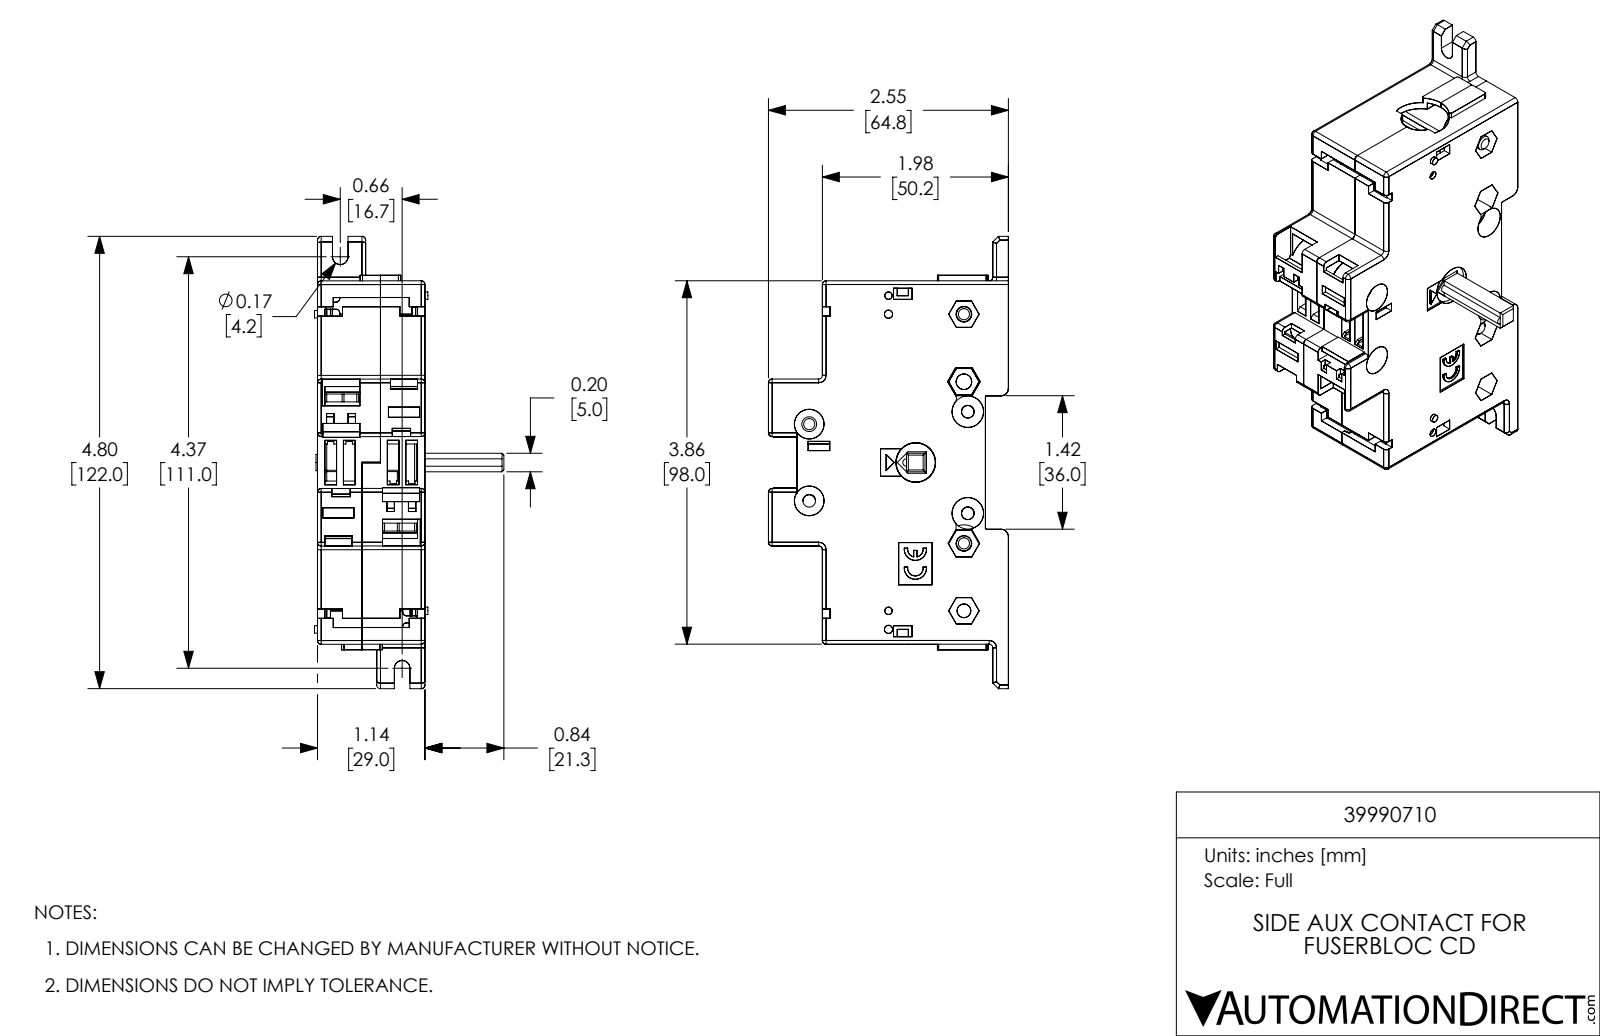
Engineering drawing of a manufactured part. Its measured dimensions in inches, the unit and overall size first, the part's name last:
Units: inches
Overall size (bounding box): 4.803 × 2.549 × 2.012
Round holes (diameter × count): ⌀0.134 ×12, ⌀0.087 ×8, ⌀0.165 ×8, ⌀0.315 ×6, ⌀0.335 ×6, ⌀0.421 ×5, ⌀0.146 ×4, ⌀0.039 ×3, ⌀0.276 ×1
Round bosses / shafts (diameter × count): ⌀0.079 ×8, ⌀0.284 ×3, ⌀0.157 ×3, ⌀0.91 ×1, ⌀0.669 ×1, ⌀0.445 ×1, ⌀0.413 ×1
Partial cylindrical surfaces — rounded edges, fillets, slot ends (radius × count): R0.02 ×136, R0.039 ×91, R0.083 ×12, R0.244 ×12, R0.118 ×8, R0.012 ×6, R0.079 ×6, R0.146 ×6
Main face-to-face distances: 0.079, 1.063, 1.142, 0.984, 0.394, 0.472, 0.669, 1.898, 0.591, 0.197
Hole centre spacings: 1.69, 1.203, 0.801, 0.772, 1.036, 1.656, 1.704, 1.933
Volume: 6.994 in³ · Surface area: 178.8 in²
Bodies: 10 solids, 2460 faces (1513 planar, 735 cylindrical, 212 other)
Part name (STEP PRODUCT): 39990710
STEP written by: SolidWorks 2017 (AUTOMOTIVE_DESIGN)
